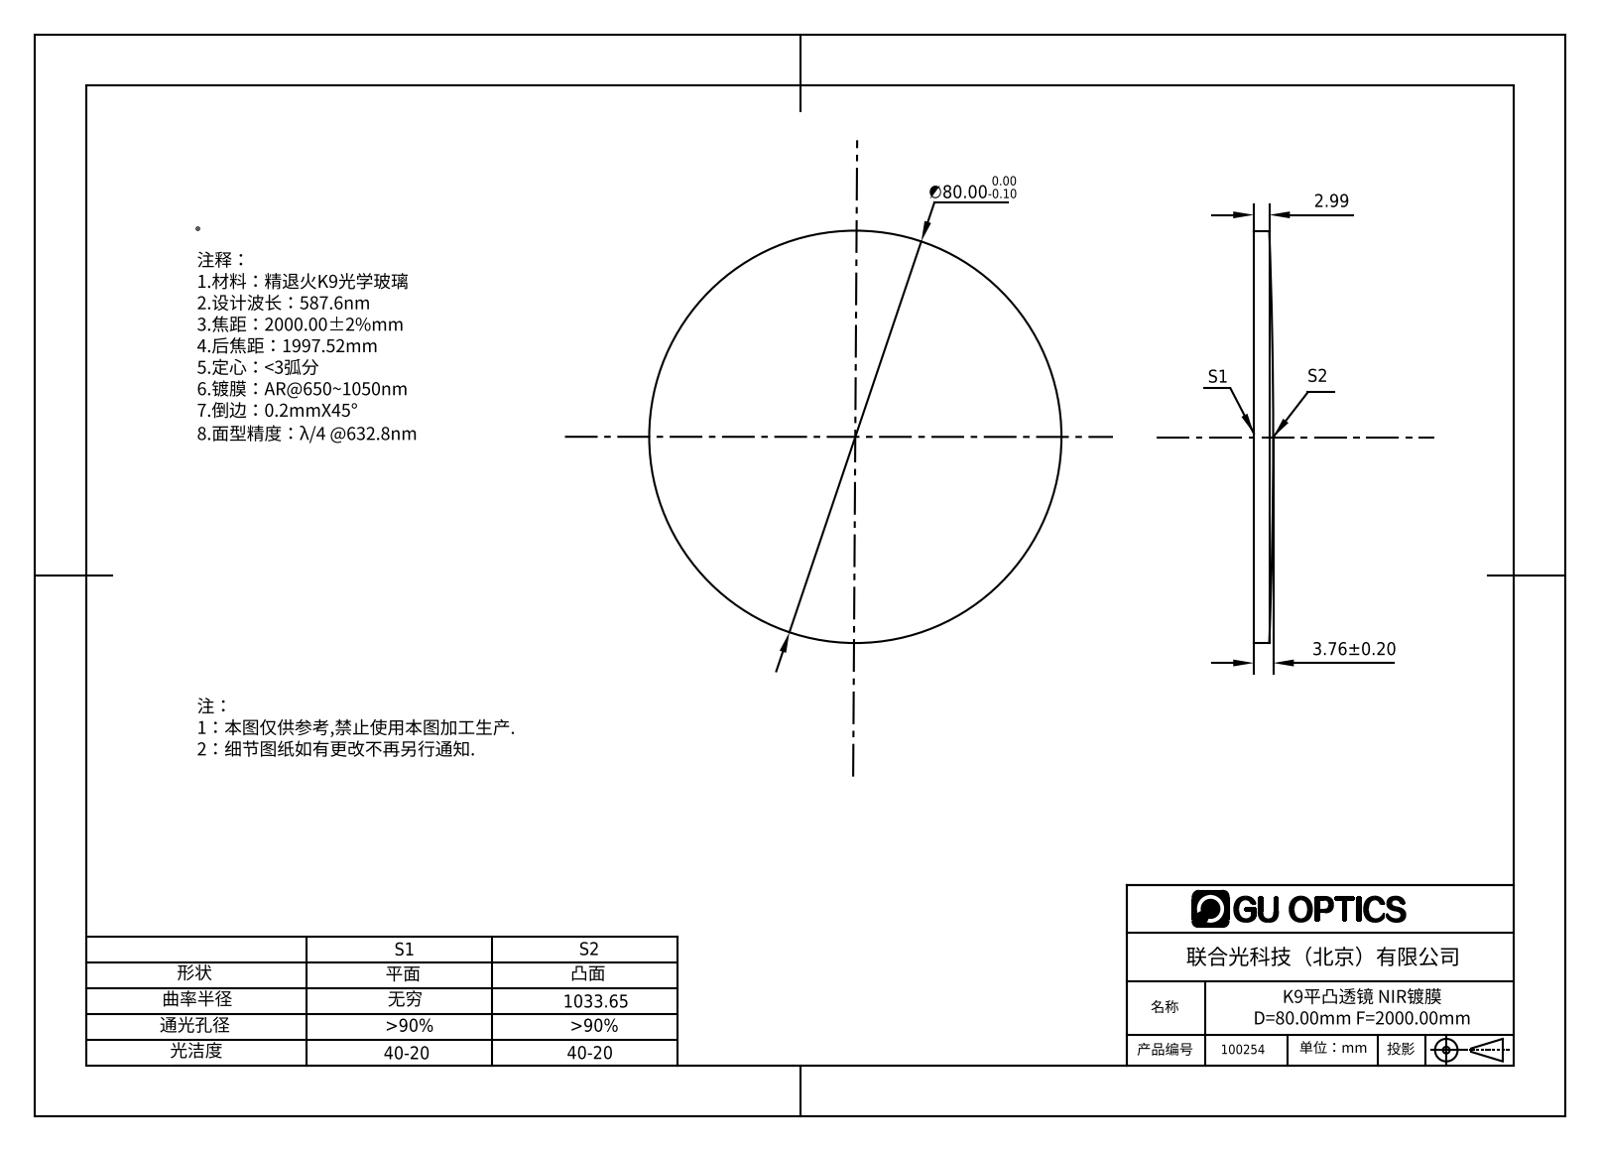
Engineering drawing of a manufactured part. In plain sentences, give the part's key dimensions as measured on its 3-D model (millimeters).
The part is named "100082". Its 3-D file was written by "SolidWorks 2016 (AUTOMOTIVE_DESIGN)". It is 1 solid with 5 faces: 1 planar, 2 cylindrical and 2 other. Overall it measures 80 by 80 by 3.76 millimeters. Its volume is 16 965 cubic millimeters and its surface area 10 806 square millimeters. Round bosses or shafts: 1 of diameter 80.
